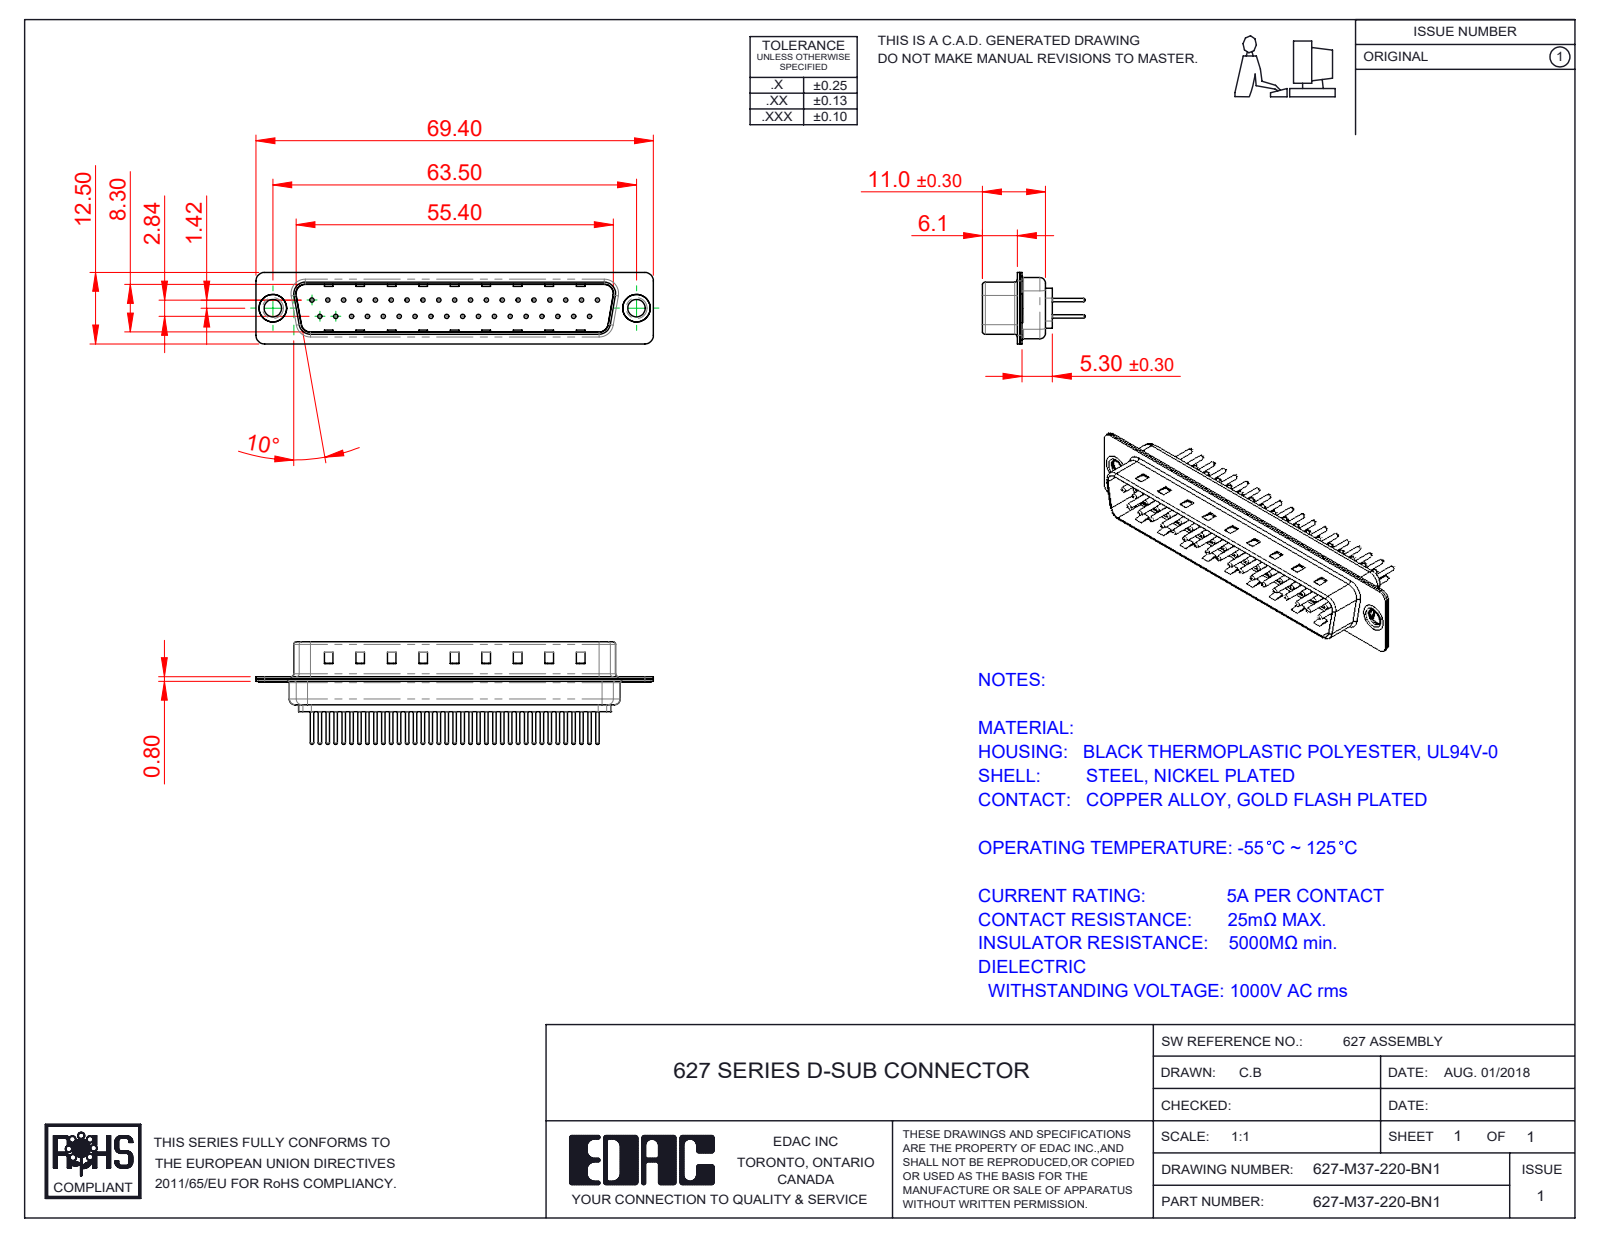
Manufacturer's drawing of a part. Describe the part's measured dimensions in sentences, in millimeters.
The part is named "627M Shell Front_37 Contacts; 627M Contact Row 2_20; 627M Contact Row 1_20; 627M Housing_37 Contacts (+3 more)". Its 3-D file was written by "SolidWorks 2020 (CONFIG_CONTROL_DESIGN)". It is 42 solids with 1755 faces: 462 planar, 643 cylindrical and 650 other. Overall it measures 69.4 by 17.9 by 12.5 millimeters. Its volume is 3 690 cubic millimeters and its surface area 9 124 square millimeters. Round holes: 37 of diameter 0.75, 37 of diameter 1.6, 37 of diameter 2, 2 of diameter 3.05, 2 of diameter 4, 2 of diameter 4.8. Round bosses or shafts: 37 of diameter 1.5, 37 of diameter 0.6, 2 of diameter 5, 2 of diameter 4.9, 2 of diameter 3.55. Partial cylindrical surfaces (rounded edges, fillets, slot ends): 16 of radius 1.5, 12 of radius 2, 8 of radius 0.5, 8 of radius 1.6, 4 of radius 0.25, 4 of radius 0.6, 4 of radius 0.65, 4 of radius 0.9. The main face-to-face distances are 0.4, 0.8, 9.5, 9.1, 8.7, 9.9, 1.2, 5.7, 0.75, 0.35. The hole center spacings are 2.77, 5.54, 3.16, 8.31, 11.08, 13.85, 16.62, 19.39.
